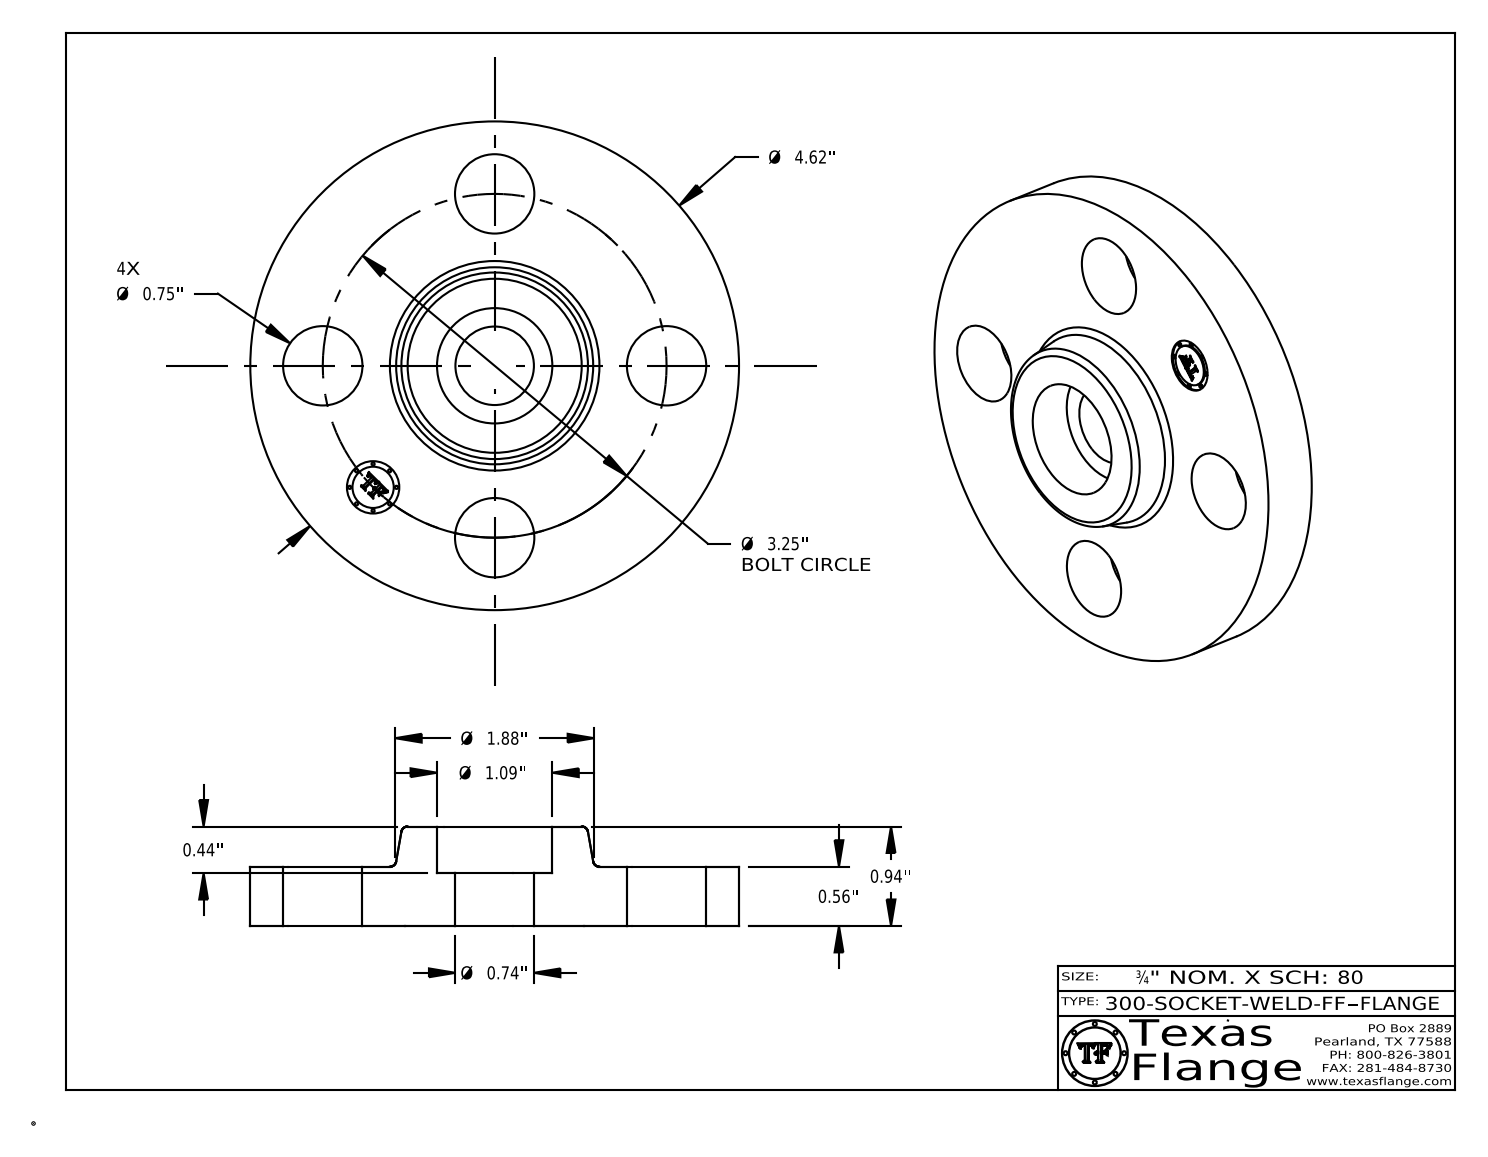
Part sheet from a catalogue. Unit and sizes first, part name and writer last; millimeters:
Units: millimetres
Overall size (bounding box): 117.3 × 117.3 × 23.9
Round holes (diameter × count): ⌀19.1 ×4, ⌀12.6 ×1, ⌀18.8 ×1, ⌀27.7 ×1
Round bosses / shafts (diameter × count): ⌀0.8 ×8, ⌀117.3 ×1, ⌀9.9 ×1
Main face-to-face distances: 14.2, 23.9, 9.7, 12.7, 1.5, 11.2, 13.8, 1.1, 0.4, 10
Hole centre spacings: 41.3, 58.4, 31.6, 76.3, 82.6
Volume: 143 400 mm³ · Surface area: 30 270 mm²
Bodies: 1 solid, 410 faces (370 planar, 34 cylindrical, 6 other)
Part name (STEP PRODUCT): 300-SOCKET-WELD-FF
STEP written by: CATIA V5 STEP AP214 (AUTOMOTIVE_DESIGN)
